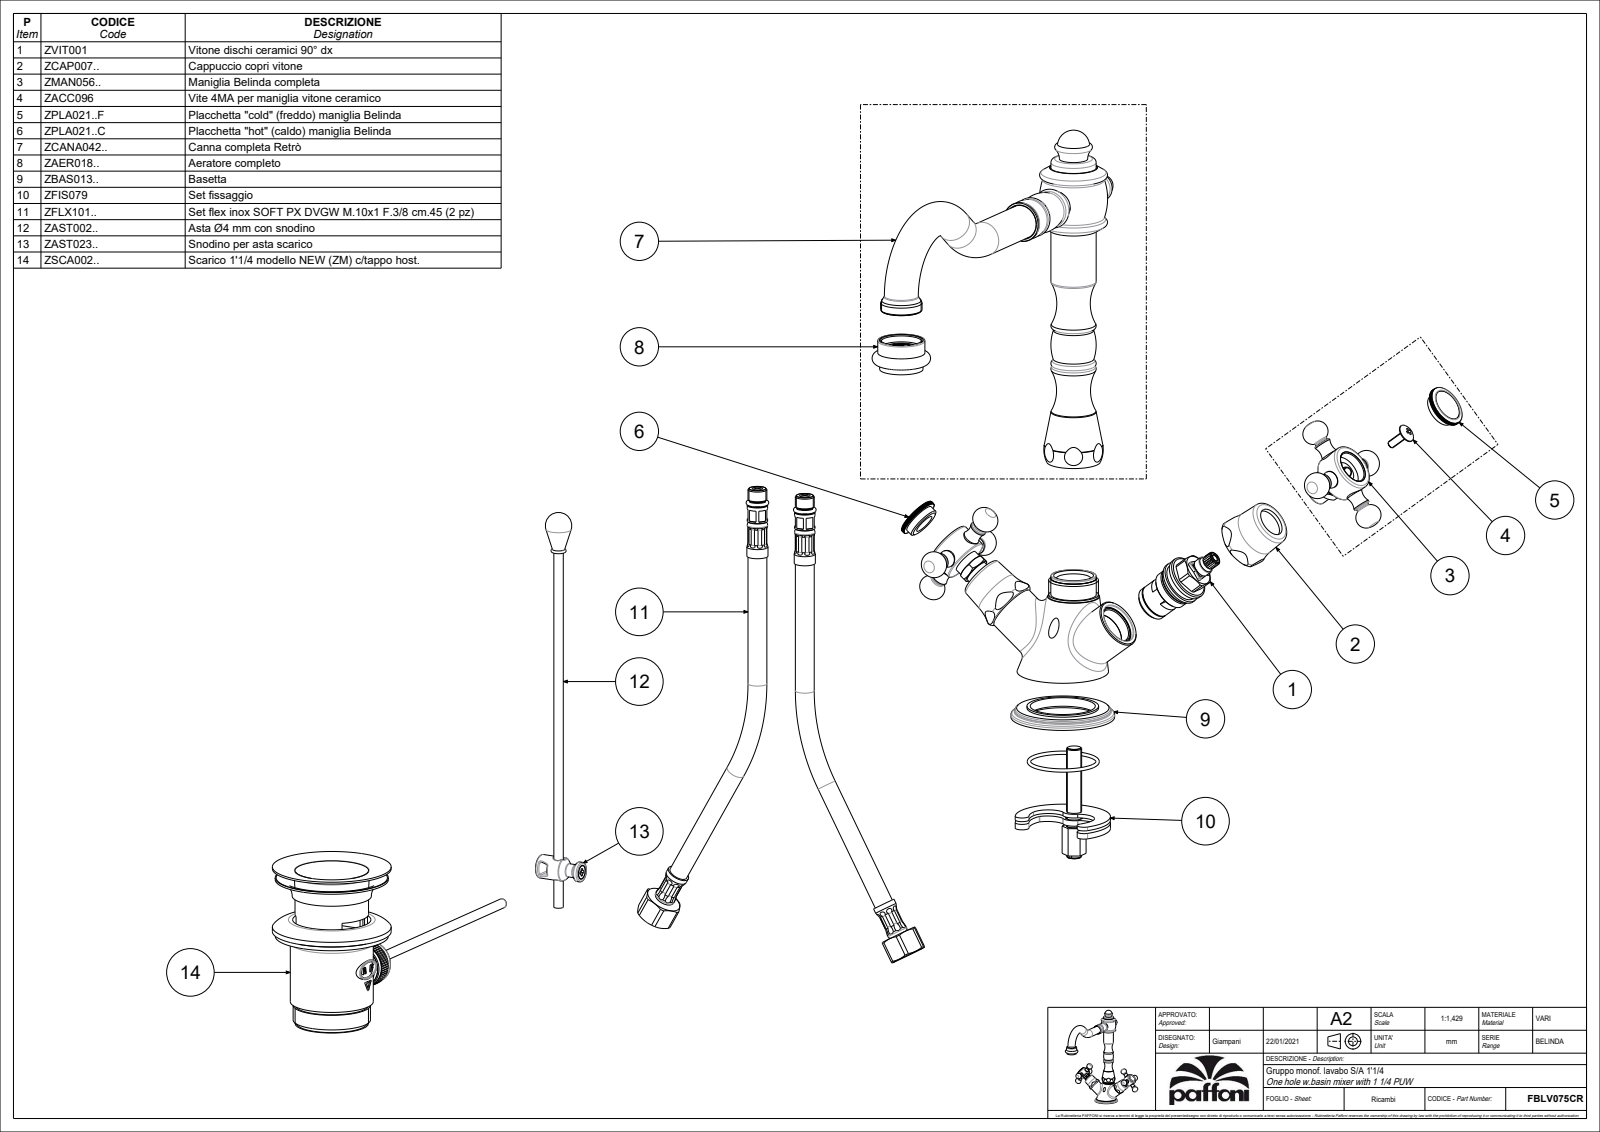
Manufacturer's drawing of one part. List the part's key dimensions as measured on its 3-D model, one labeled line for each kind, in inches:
Part name (STEP PRODUCT): FBLV075CR
STEP written by: CREO PARAMETRIC BY PTC INC, 2020044 (CONFIG_CONTROL_DESIGN)
Units: inches
Bodies: 4 solids, 1347 faces (577 planar, 400 cylindrical, 370 other)
Overall size (bounding box): 9.241 × 9.031 × 6.912
Volume: 15.01 in³ · Surface area: 115.3 in²
Round holes (diameter × count): ⌀0.354 ×4, ⌀0.433 ×2, ⌀0.61 ×2, ⌀0.709 ×2, ⌀0.748 ×2, ⌀0.827 ×2, ⌀0.846 ×2, ⌀0.898 ×2, ⌀1.004 ×2, ⌀0.217 ×1, ⌀0.236 ×1, ⌀0.268 ×1
Round bosses / shafts (diameter × count): ⌀0.354 ×6, ⌀0.276 ×6, ⌀0.984 ×3, ⌀1.035 ×2, ⌀0.709 ×2, ⌀0.551 ×2, ⌀0.512 ×2, ⌀2.165 ×1
Partial cylindrical surfaces — rounded edges, fillets, slot ends (radius × count): R0.138 ×2, R0.433 ×2
Main face-to-face distances: 0.197, 0.196, 0.079, 0.051, 2.252, 6.126, 0.449, 6.323, 6.322, 1.804
Hole centre spacings: 0.276, 0.465, 0.527, 0.547, 0.024, 0.374, 0.449, 0.472
